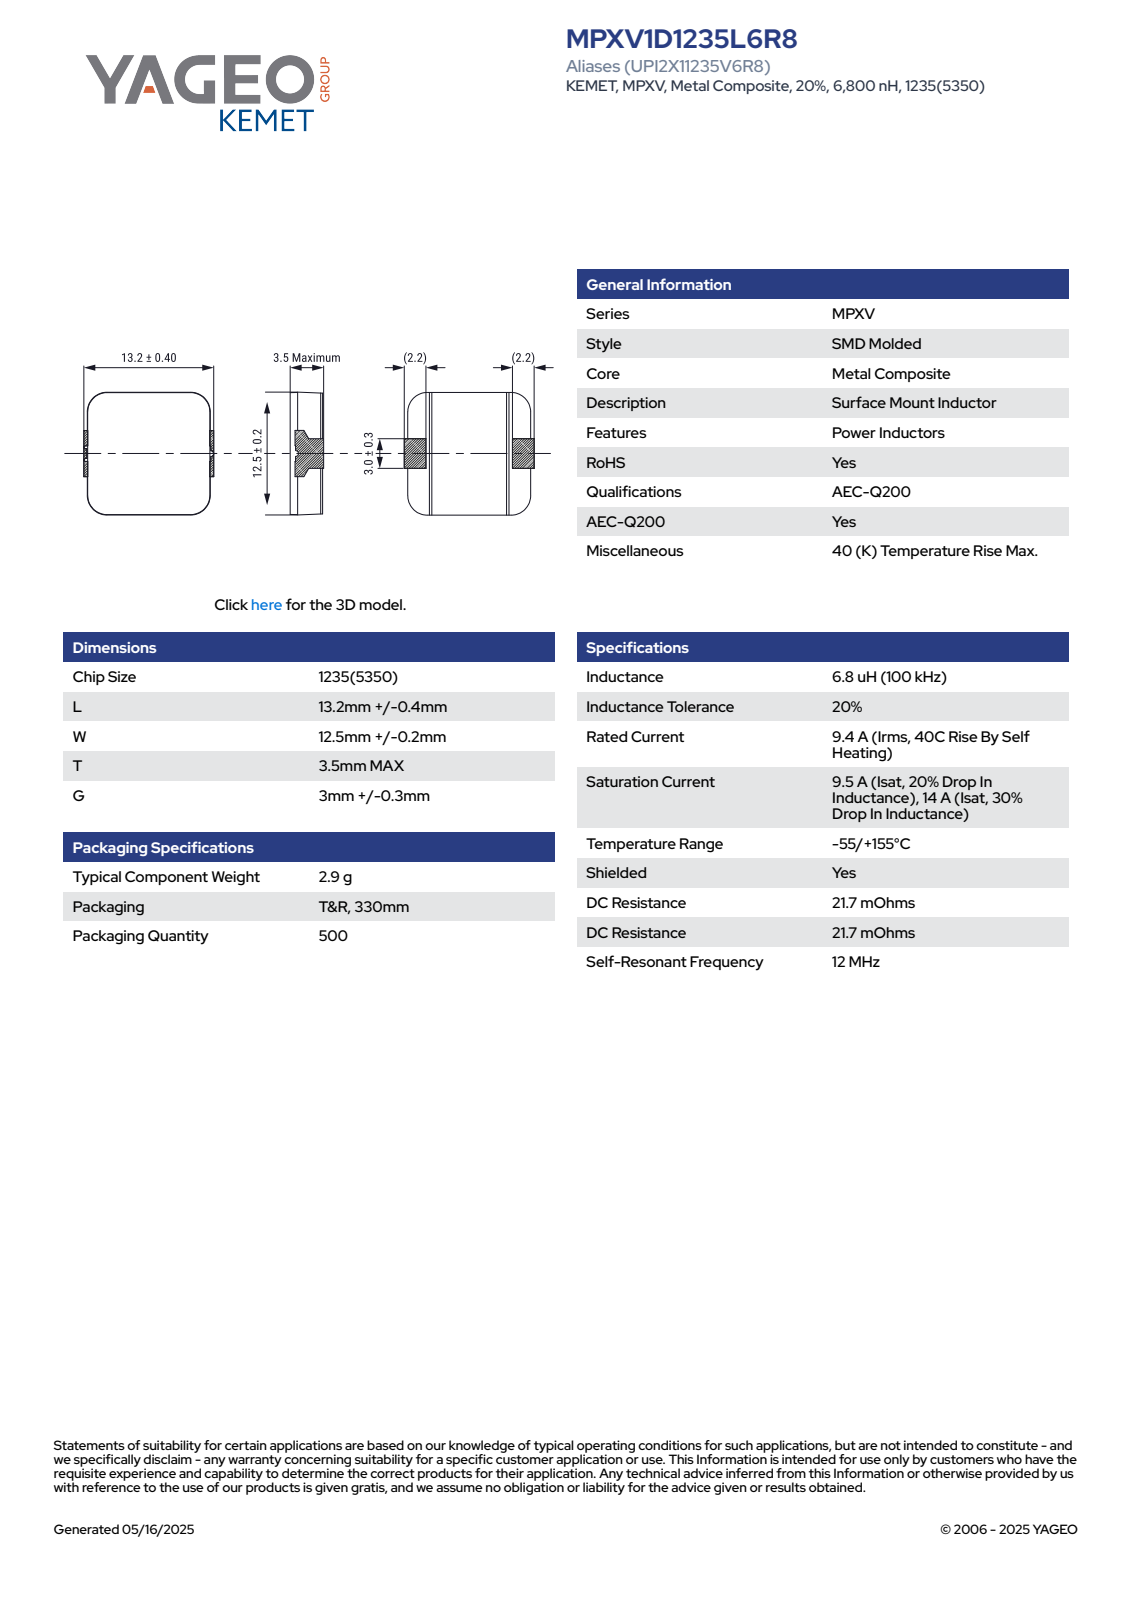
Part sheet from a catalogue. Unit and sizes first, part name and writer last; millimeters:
Units: millimetres
Overall size (bounding box): 13.6 × 12.7 × 3.56
Partial cylindrical surfaces — rounded edges, fillets, slot ends (radius × count): R0.26 ×4, R1.96 ×4, R2 ×4, R0.15 ×3
Main face-to-face distances: 3.5, 3.3, 13.34, 3.56, 13.6, 13.08, 2.6, 2.54, 2.34, 0.96
Volume: 542 mm³ · Surface area: 525 mm²
Bodies: 1 solid, 130 faces (113 planar, 17 cylindrical, 0 other)
Part name (STEP PRODUCT): MPX1D1235(3_0)(KEMET)SLDPRT
STEP written by: SolidWorks 2018 (AUTOMOTIVE_DESIGN)
